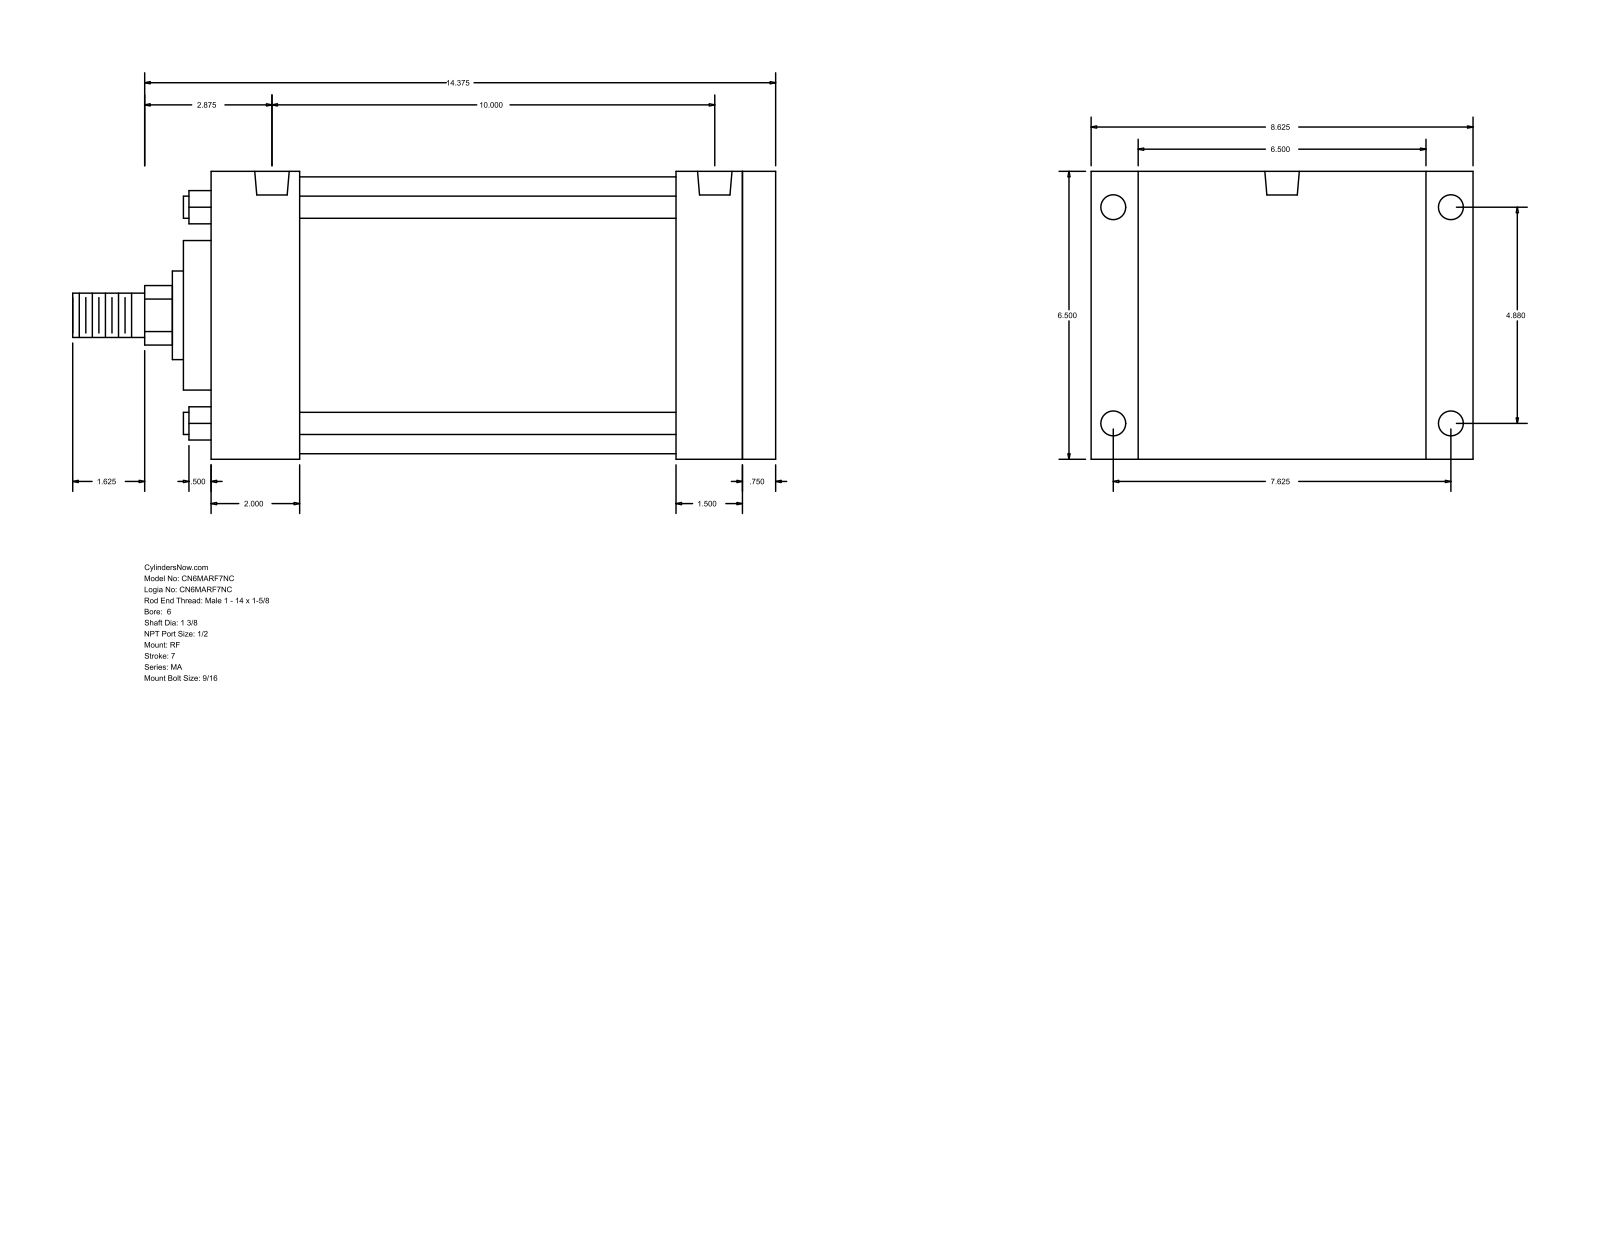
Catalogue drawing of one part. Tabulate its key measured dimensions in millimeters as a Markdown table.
| quantity | value |
| --- | --- |
| part name | MA_RF__0600_1.375 |
| STEP written by | GSSL Pune (CONFIG_CONTROL_DESIGN) |
| units | millimeters |
| bodies | 0 solids, 94 faces (65 planar, 29 cylindrical, 0 other) |
| overall size | 406.4 × 219.07 × 165.1 |
| round holes (diameter × count) | 14.29 × 4, 17.46 × 4, 19.77 × 2 |
| round bosses / shafts (diameter × count) | 12.7 × 4, 158.75 × 1, 85.72 × 1, 50.8 × 1, 34.92 × 1, 25.4 × 1 |
| partial cylindrical surfaces (radius × count) | 17.06 × 1 |
| main face-to-face distances | 165.1, 327.02, 219.08, 19.05, 307.97, 50.8, 257.17, 276.22, 269.88, 38.09 |
| hole center spacings | 123.96, 193.68, 229.95, 257.17, 3.18, 253.99 |
